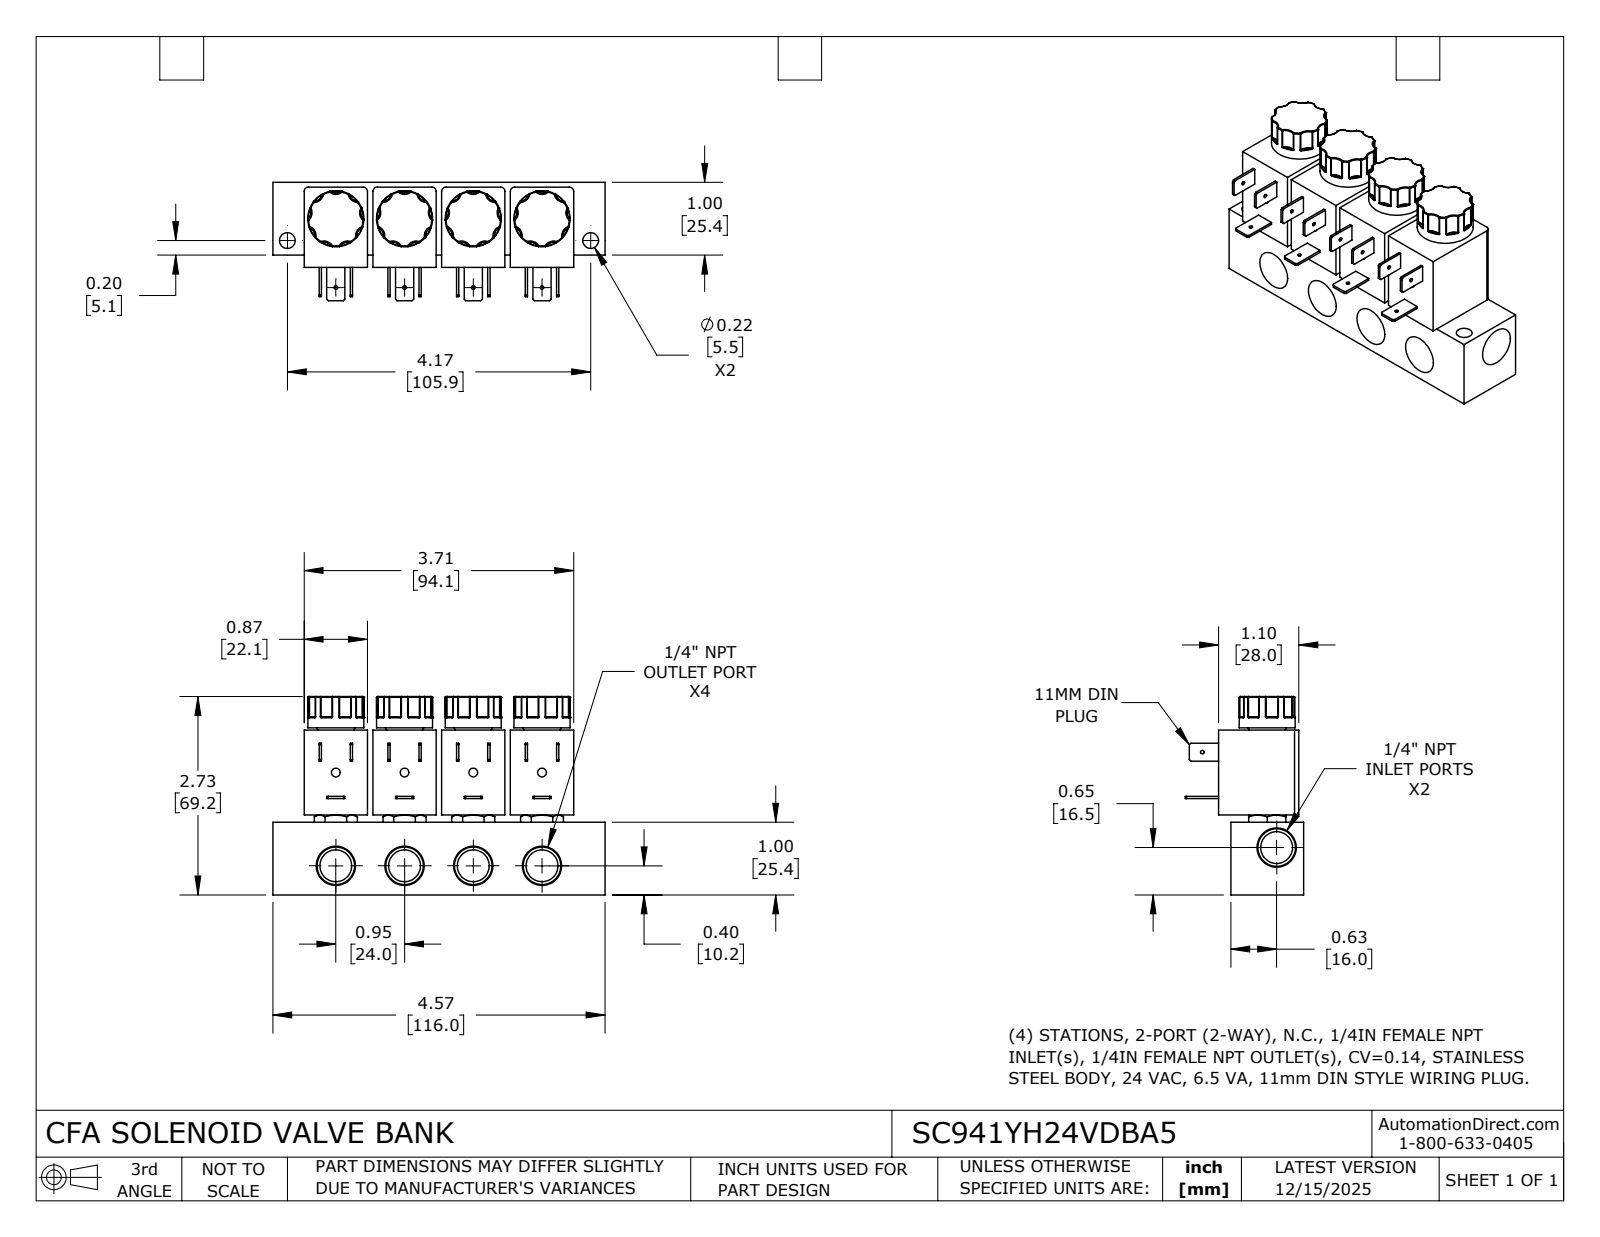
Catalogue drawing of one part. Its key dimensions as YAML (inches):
part_name: "SC941YH24VDBA5"
step_written_by: "SolidWorks 2024 (CONFIG_CONTROL_DESIGN)"
units: inches
bodies: {solids: 1, faces: 868, planar: 192, cylindrical: 184, other: 492}
overall_size: [4.567, 2.725, 1.627]
volume: 9.182
surface_area: 61.05
round_holes:
  - {diameter: 0.05, count: 5}
  - {diameter: 0.438, count: 5}
  - {diameter: 0.12, count: 4}
  - {diameter: 0.217, count: 2}
round_bosses_or_shafts:
  - {diameter: 0.77, count: 4}
partial_cylinders:
  - {radius: 0.01, count: 72}
  - {radius: 0.133, count: 34}
  - {radius: 0.06, count: 8}
  - {radius: 0.132, count: 2}
face_to_face_distances: [1, 0.945, 1.169, 1.89, 1.815, 0.87, 0.169, 0.065, 0.935, 1.104]
hole_center_spacings: [0.945, 1.282, 1.593, 0.945, 1.89, 1.89, 2.835, 1.593]
